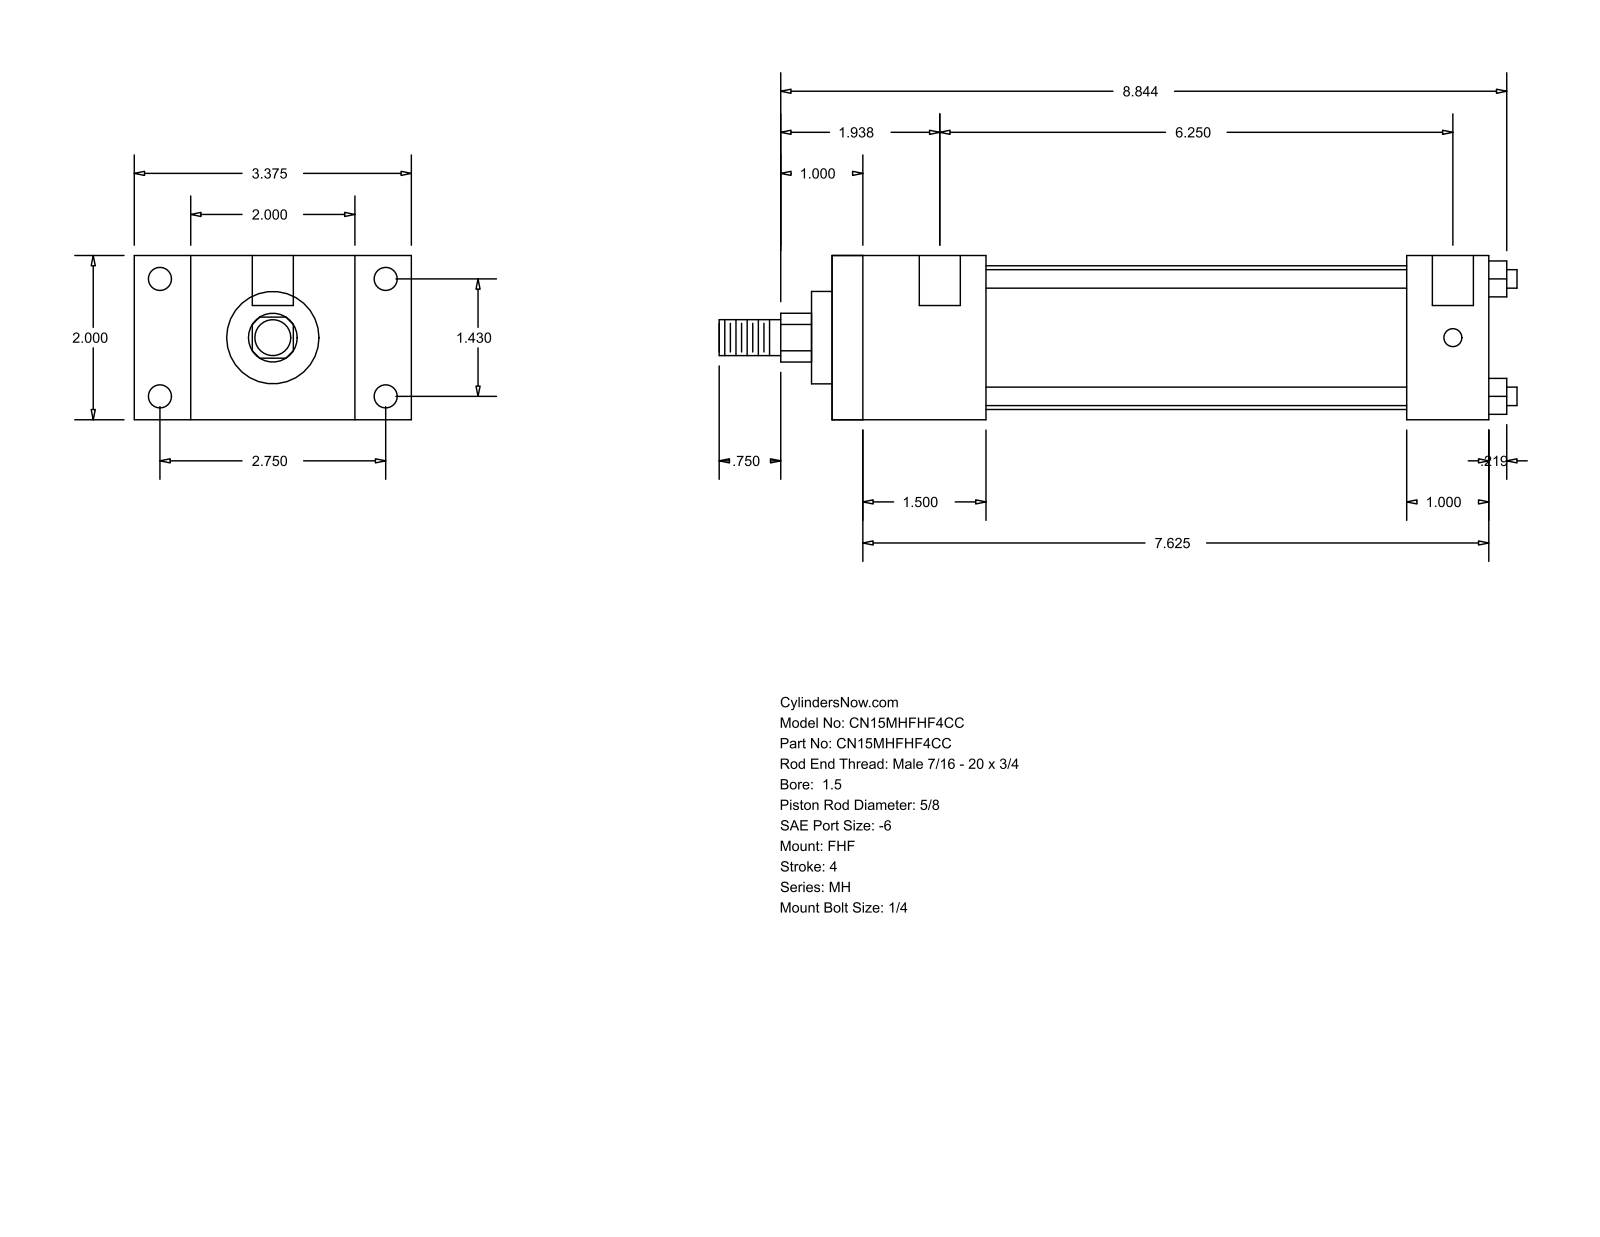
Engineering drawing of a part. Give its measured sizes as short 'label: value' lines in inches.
name: MH_FHF__0150_0.625
written by: GSSL Pune (CONFIG_CONTROL_DESIGN)
unit: in
bodies: 0 solids, 88 faces (60 planar, 28 cylindrical, 0 other)
size: 9.719 × 3.375 × 2
holes: 4× ⌀0.219, 4× ⌀0.281, 2× ⌀0.5
bosses: 4× ⌀0.225, 1× ⌀1.75, 1× ⌀1.125, 1× ⌀0.625, 1× ⌀0.437
rounds: 1× R0.297
face distances: 2, 0.687, 2.687, 1.875, 3.375, 8, 6.125, 7, 5.125, 1
hole spacings: 1.43, 2.75, 3.099, 6.375, 0.125, 6.25
